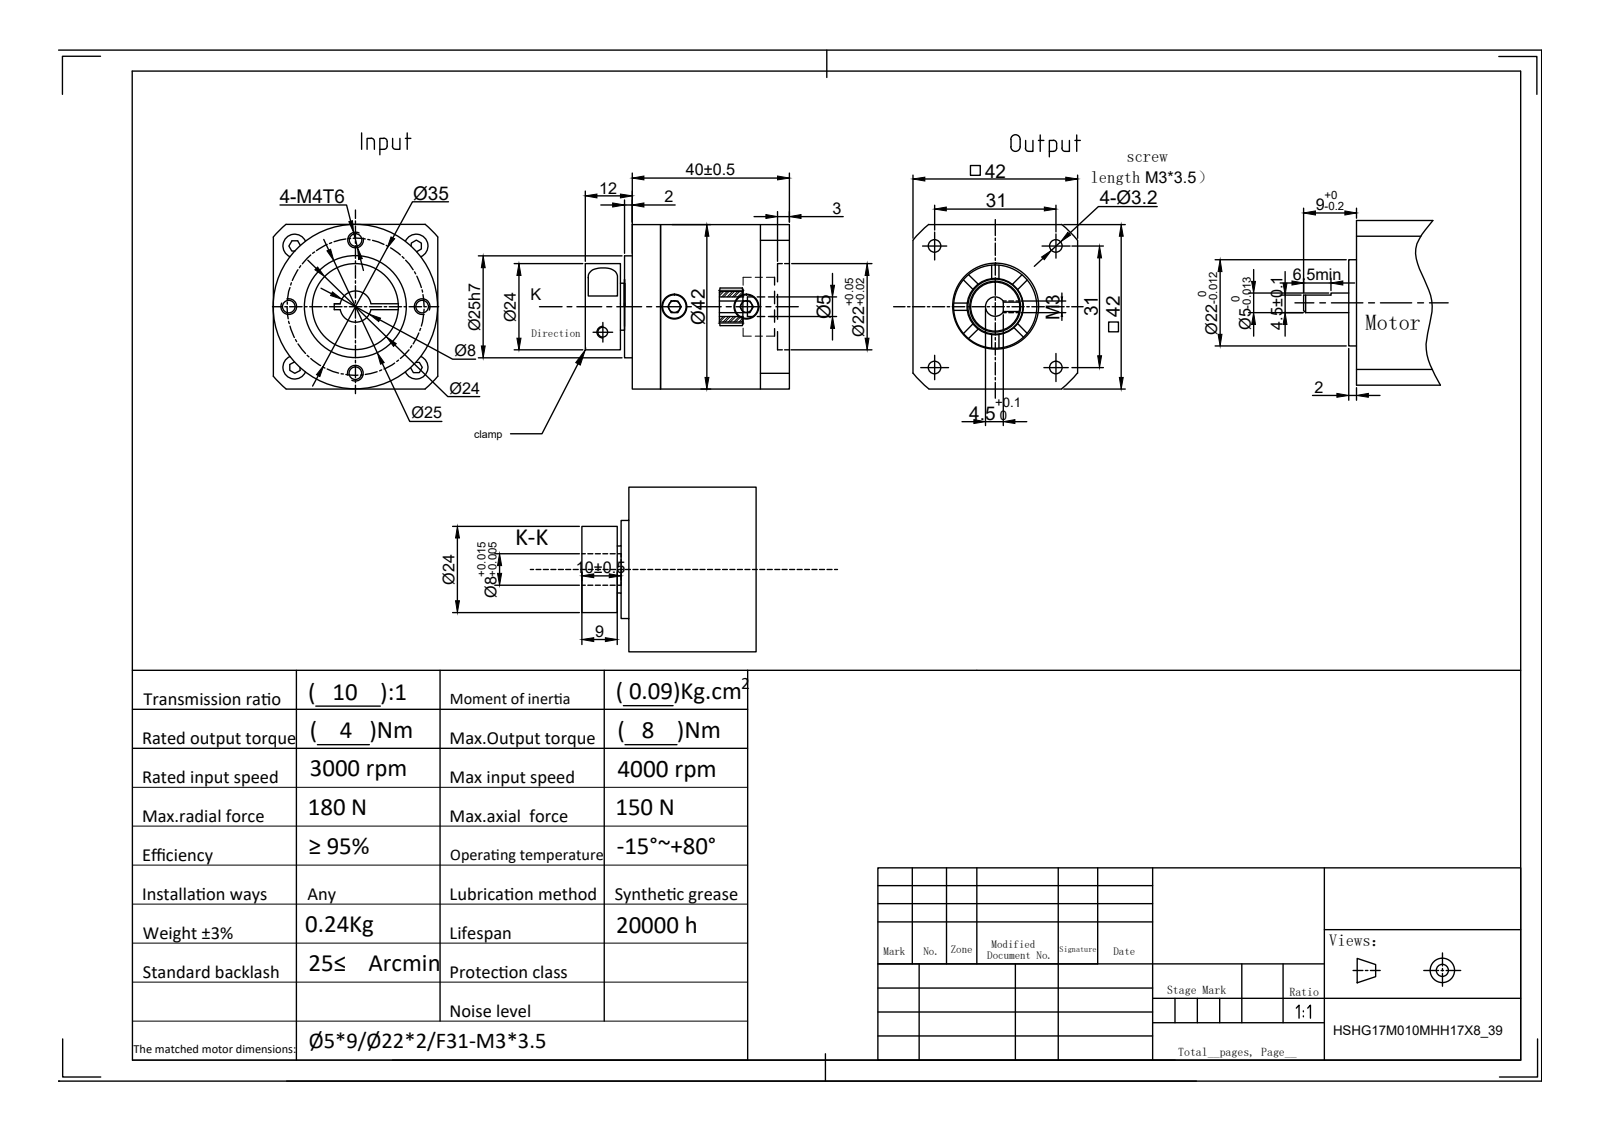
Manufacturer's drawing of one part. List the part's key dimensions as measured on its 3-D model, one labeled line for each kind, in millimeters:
Part name (STEP PRODUCT): HSHG17M010MHH17X8_39
STEP written by: SolidWorks 2018 (AUTOMOTIVE_DESIGN)
Units: millimetres
Bodies: 7 solids, 310 faces (132 planar, 85 cylindrical, 93 other)
Overall size (bounding box): 55.5 × 42 × 42
Volume: 61 165 mm³ · Surface area: 14 467 mm²
Round holes (diameter × count): ⌀3.2 ×5, ⌀3.3 ×4, ⌀6.5 ×4, ⌀2.5 ×2, ⌀5 ×2, ⌀4 ×1, ⌀8 ×1, ⌀15 ×1, ⌀22 ×1
Round bosses / shafts (diameter × count): ⌀3 ×6, ⌀5.5 ×5, ⌀42 ×1, ⌀25 ×1, ⌀24 ×1, ⌀14 ×1, ⌀13 ×1
Partial cylindrical surfaces — rounded edges, fillets, slot ends (radius × count): R3 ×1, R27.5 ×1
Main face-to-face distances: 42, 40, 3, 10, 37, 12, 52, 3.5, 2, 49
Hole centre spacings: 15.63, 36.46, 17.5, 21.92, 24.75, 31, 35, 43.84
